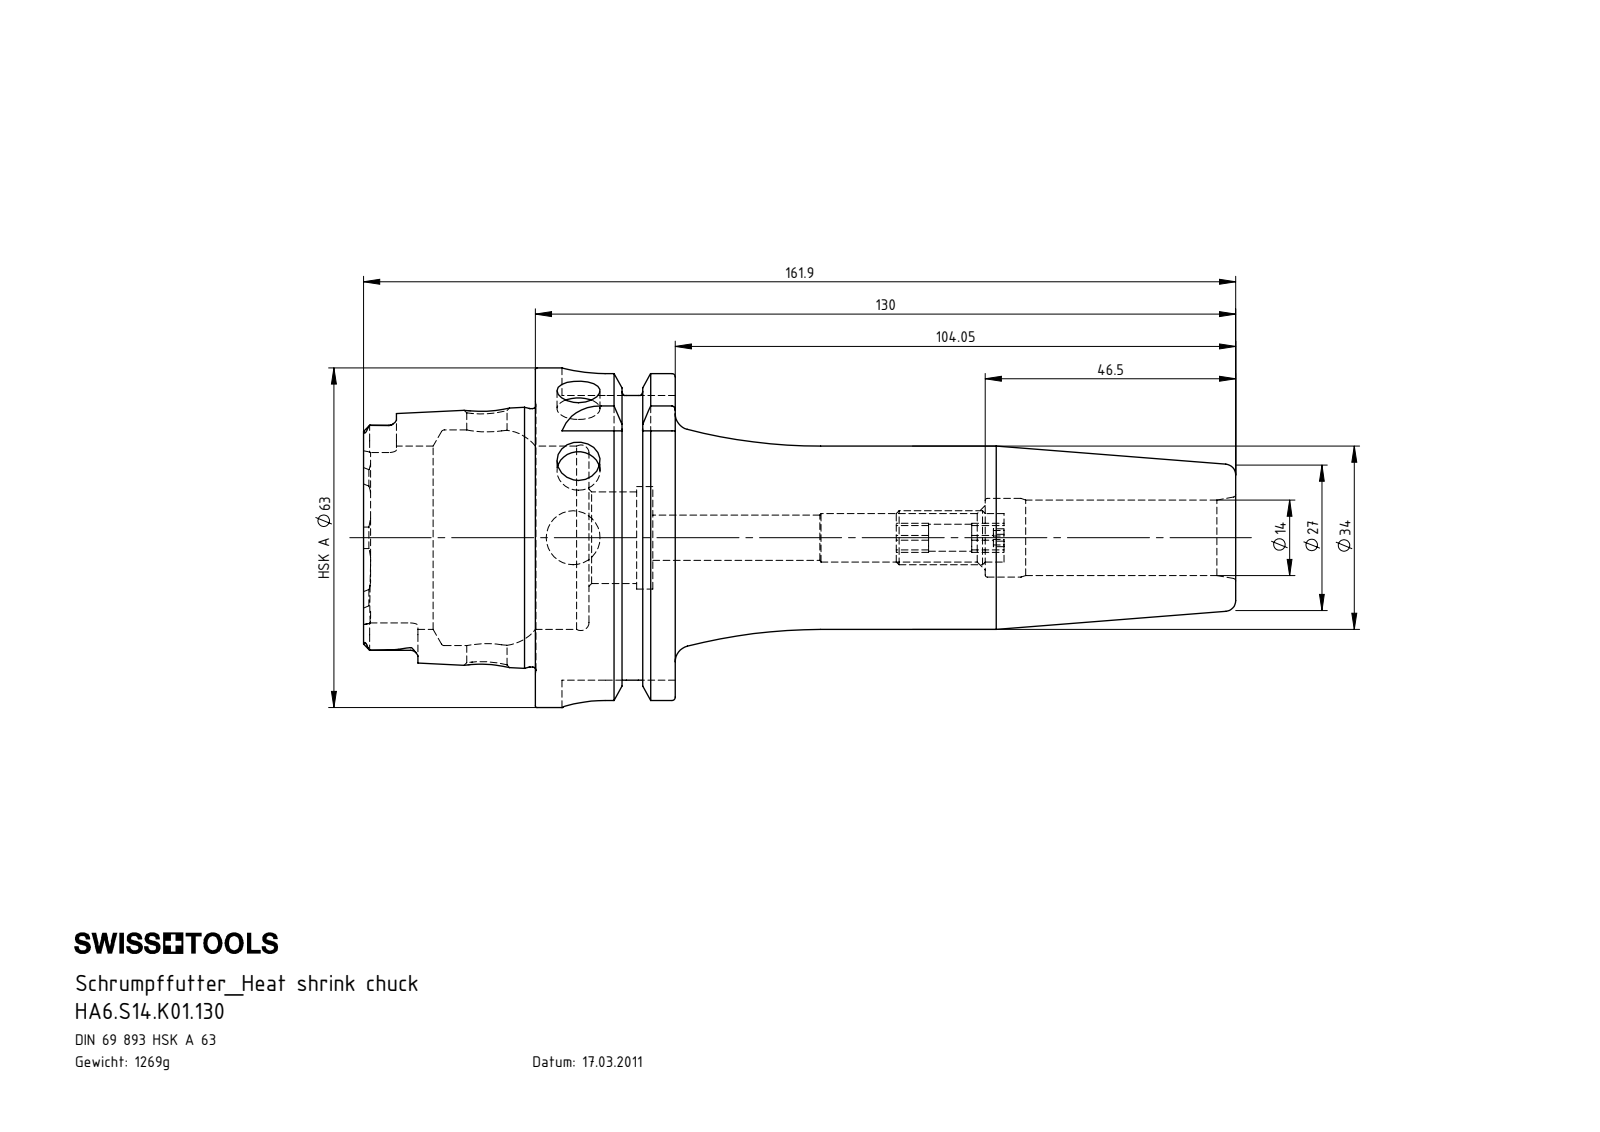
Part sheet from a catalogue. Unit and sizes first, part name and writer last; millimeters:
Units: millimetres
Overall size (bounding box): 161.9 × 63 × 63
Round holes (diameter × count): ⌀8 ×2, ⌀5 ×1, ⌀7.5 ×1, ⌀8.4 ×1, ⌀9 ×1, ⌀10 ×1, ⌀14 ×1, ⌀14.6 ×1, ⌀17 ×1, ⌀19 ×1, ⌀34 ×1, ⌀40 ×1
Round bosses / shafts (diameter × count): ⌀63 ×1, ⌀54.95 ×1, ⌀47.94 ×1, ⌀10 ×1
Partial cylindrical surfaces — rounded edges, fillets, slot ends (radius × count): R1.4 ×6, R2.88 ×4, R8 ×4
Main face-to-face distances: 25.95, 16, 9.95, 31.9, 41.85, 57.85, 52.8, 21.8, 11.85, 53.7
Volume: 161 714 mm³ · Surface area: 37 015 mm²
Bodies: 2 solids, 238 faces (82 planar, 61 cylindrical, 95 other)
Part name (STEP PRODUCT): HA6-S14.K01.130; ERU-AN4.K01.020_A; HA6-S14.K01.130_A_Fertigbearbeitung
STEP written by: SolidWorks 2012 (AUTOMOTIVE_DESIGN)
